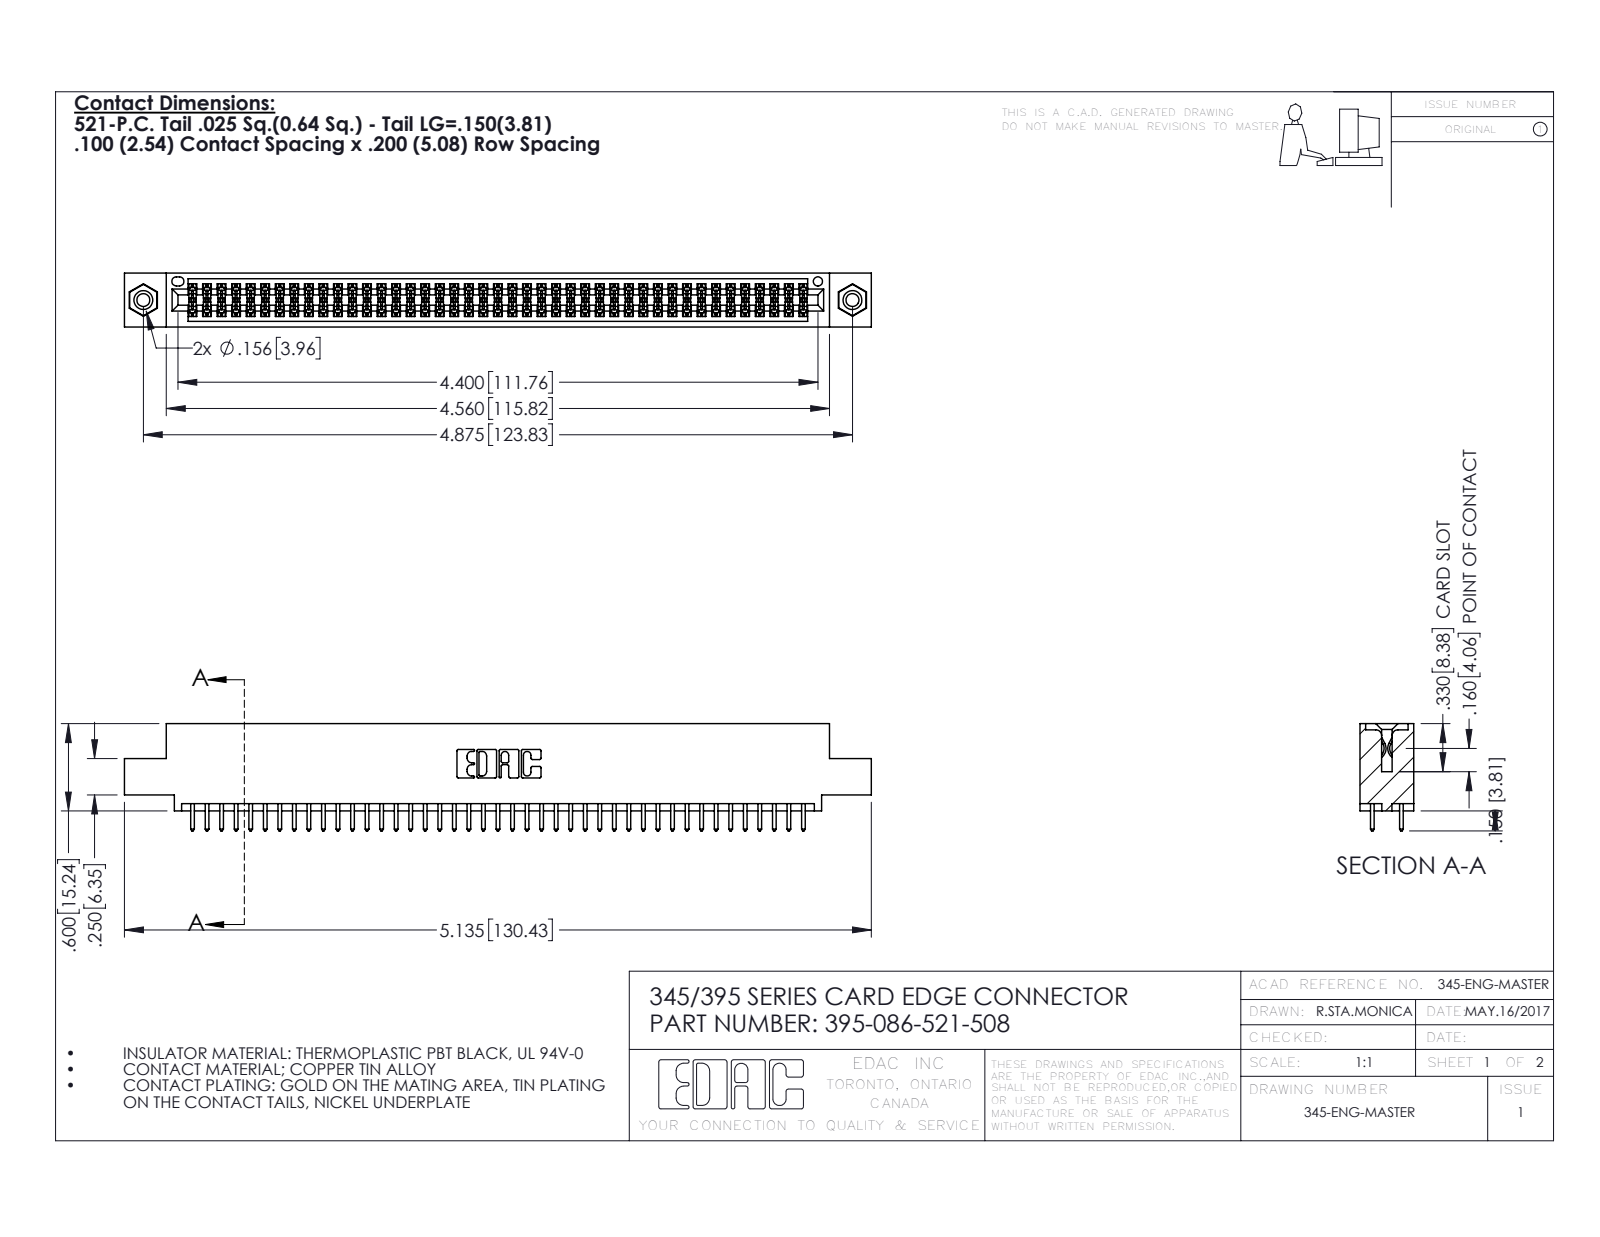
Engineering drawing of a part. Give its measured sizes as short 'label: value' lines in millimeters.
name: 345-292-001_345-293-121; 395-086-521-508; 345 Part_0.110 Offset - 0.156 Dia-TI; 345-250-001_345-250-003-102
written by: SolidWorks 2016 (CONFIG_CONTROL_DESIGN)
unit: mm
bodies: 89 solids, 4490 faces (2954 planar, 1520 cylindrical, 16 other)
size: 130.4 × 18.7 × 9.4
volume: 12 600 mm³; area: 18 470 mm²
holes: 2× ⌀2.3, 2× ⌀3.2, 2× ⌀4, 1× ⌀1.6
bosses: 2× ⌀3.9
rounds: 129× R0.2, 86× R0.3, 22× R0.3, 6× R0.2, 6× R0.8, 3× R0.7, 2× R0.4, 2× R0.5
face distances: 1.8, 7.6, 5.1, 9.4, 2.5, 6.9, 0.6, 5.7, 4.4, 3.8
hole spacings: 6.9, 117.8, 123.8
